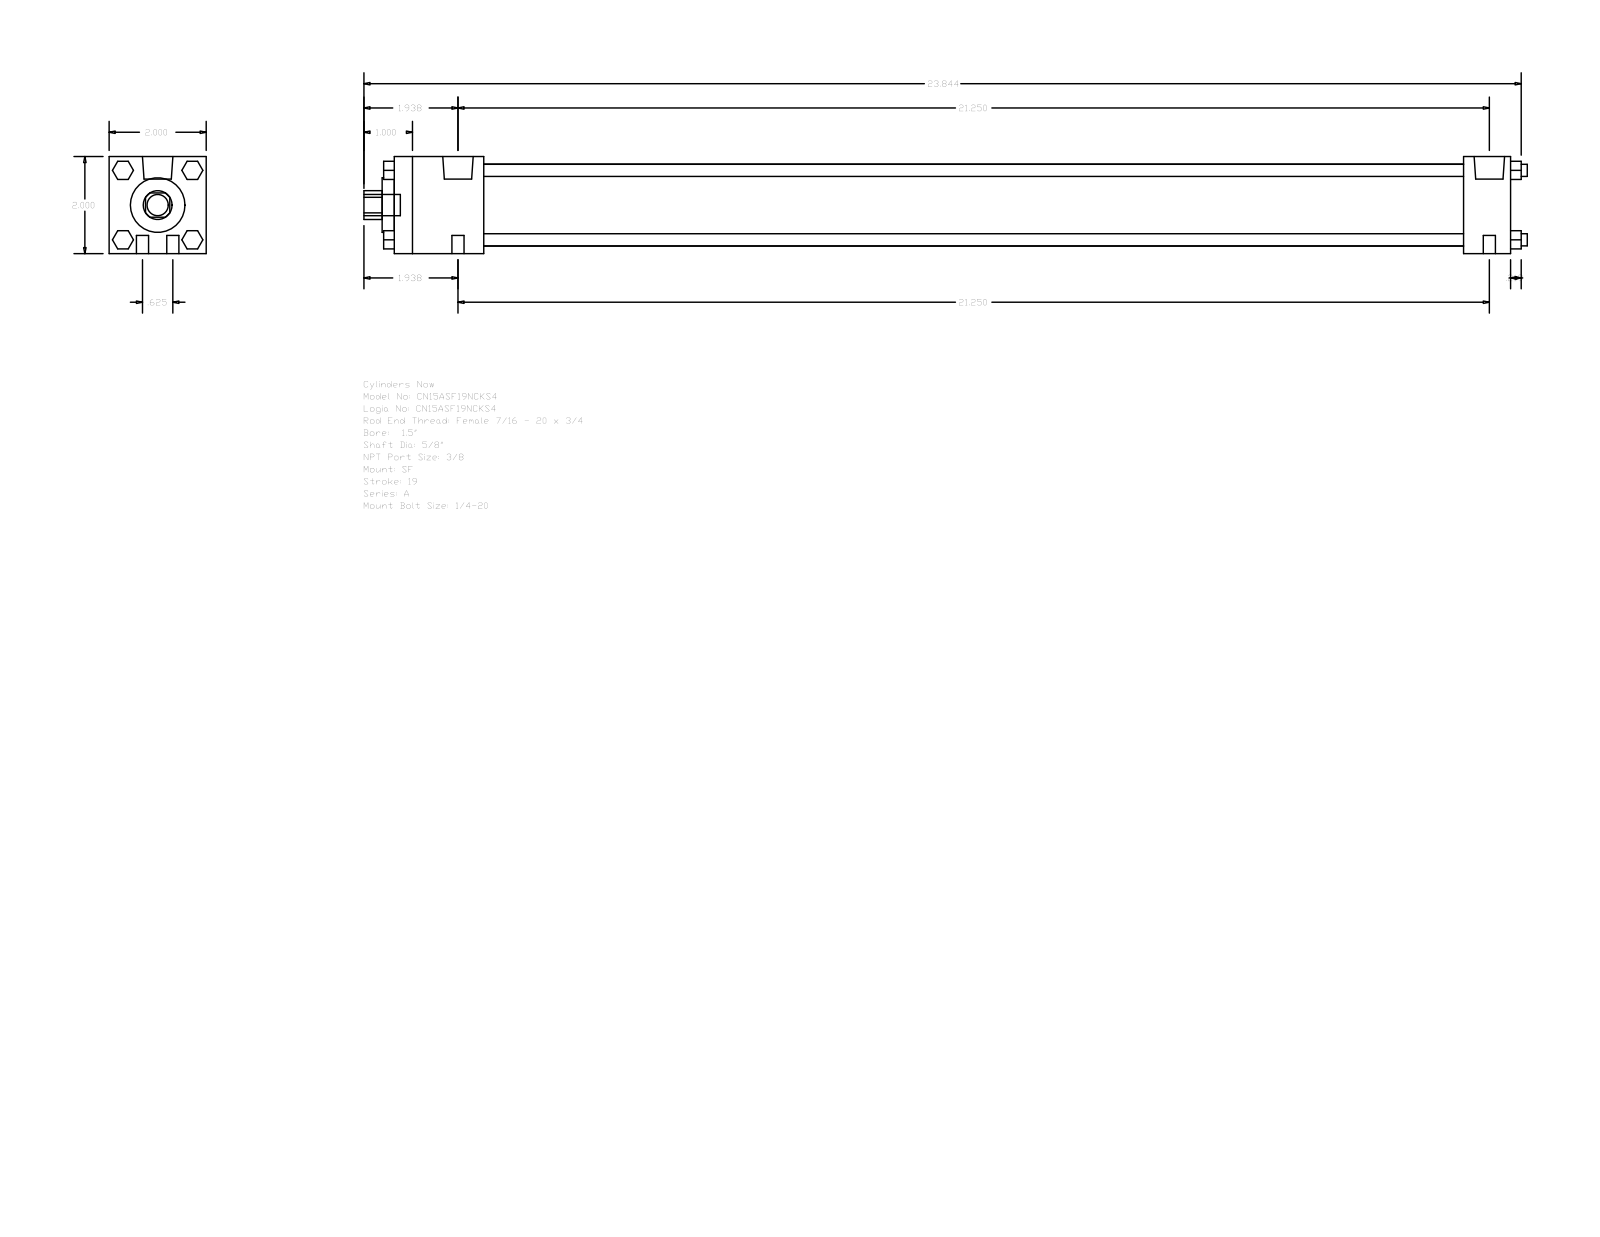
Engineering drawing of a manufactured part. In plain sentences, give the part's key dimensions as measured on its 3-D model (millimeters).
The part is named "A_SF__0150_0.625". Its 3-D file was written by "GSSL Pune (CONFIG_CONTROL_DESIGN)". It is 0 solids with 124 faces: 94 planar, 30 cylindrical and 0 other. Overall it measures 608.81 by 50.8 by 50.8 millimeters. Round holes: 1 of diameter 15.88, 1 of diameter 28.57, 1 of diameter 42.93. Round bosses or shafts: 8 of diameter 6.35, 2 of diameter 15.93, 2 of diameter 5.56, 1 of diameter 11.11. Partial cylindrical surfaces (rounded edges, fillets, slot ends): 1 of radius 7.54. The main face-to-face distances are 50.8, 584.2, 46.83, 559.59, 512.76, 537.37, 24.61, 9.52, 6.35, 53.18.
